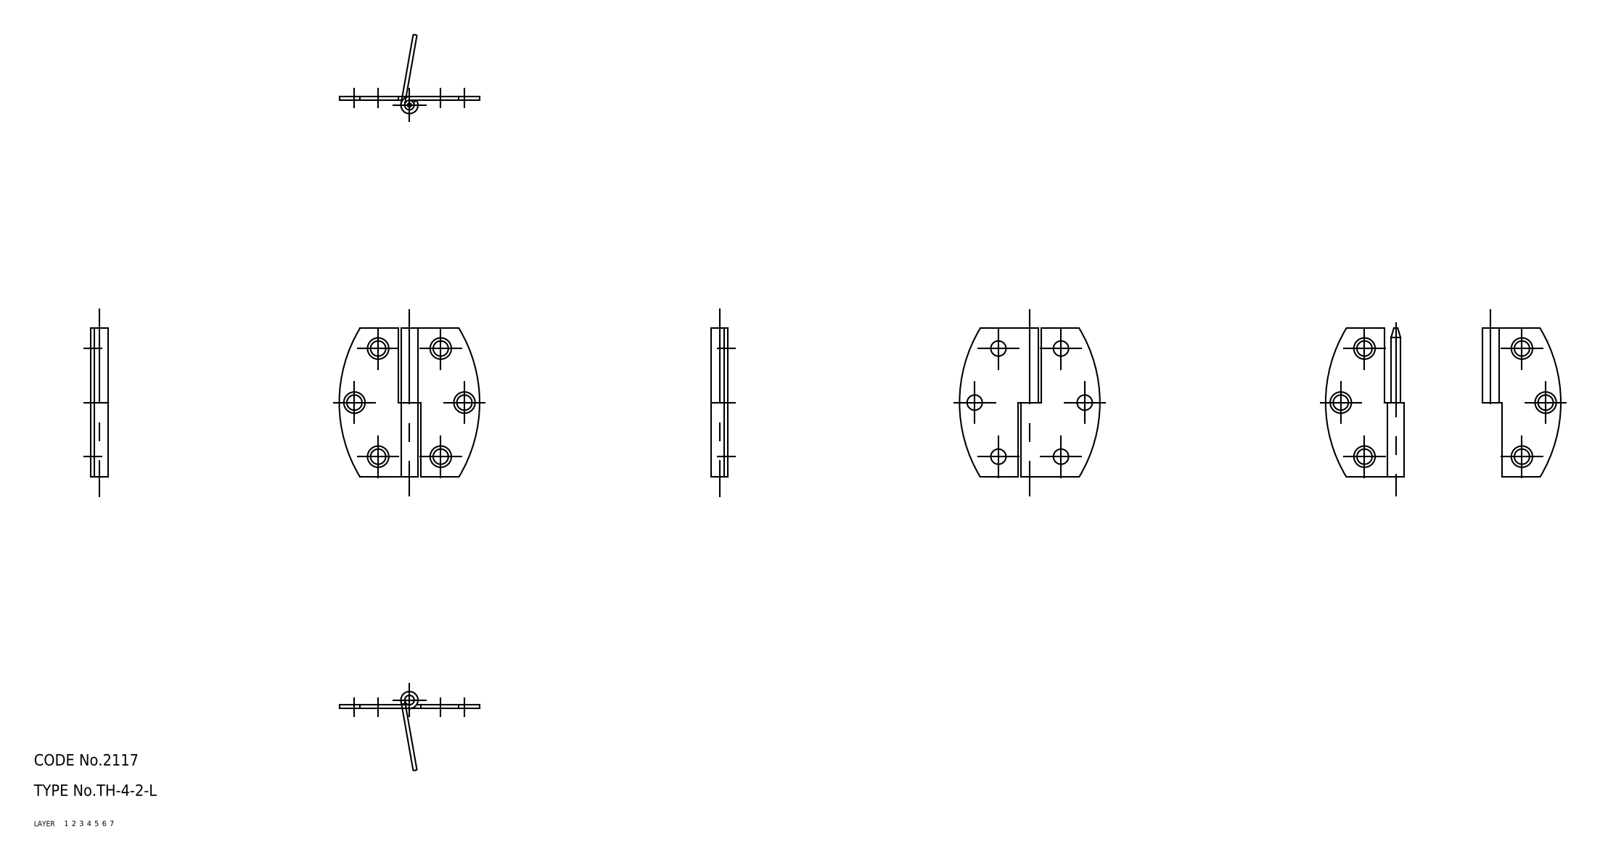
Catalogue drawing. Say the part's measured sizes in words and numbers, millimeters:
The part is named "shaft; hinge piece_B; hinge piece_A; TH_4_2_L_9094_36". Its 3-D file was written by "CADfix (AUTOMOTIVE_DESIGN)". It is 3 solids with 50 faces: 0 planar, 0 cylindrical and 50 other. Overall it measures 39.3 by 37 by 4.5 millimeters. Its volume is 1 644 cubic millimeters and its surface area 3 572 square millimeters.
